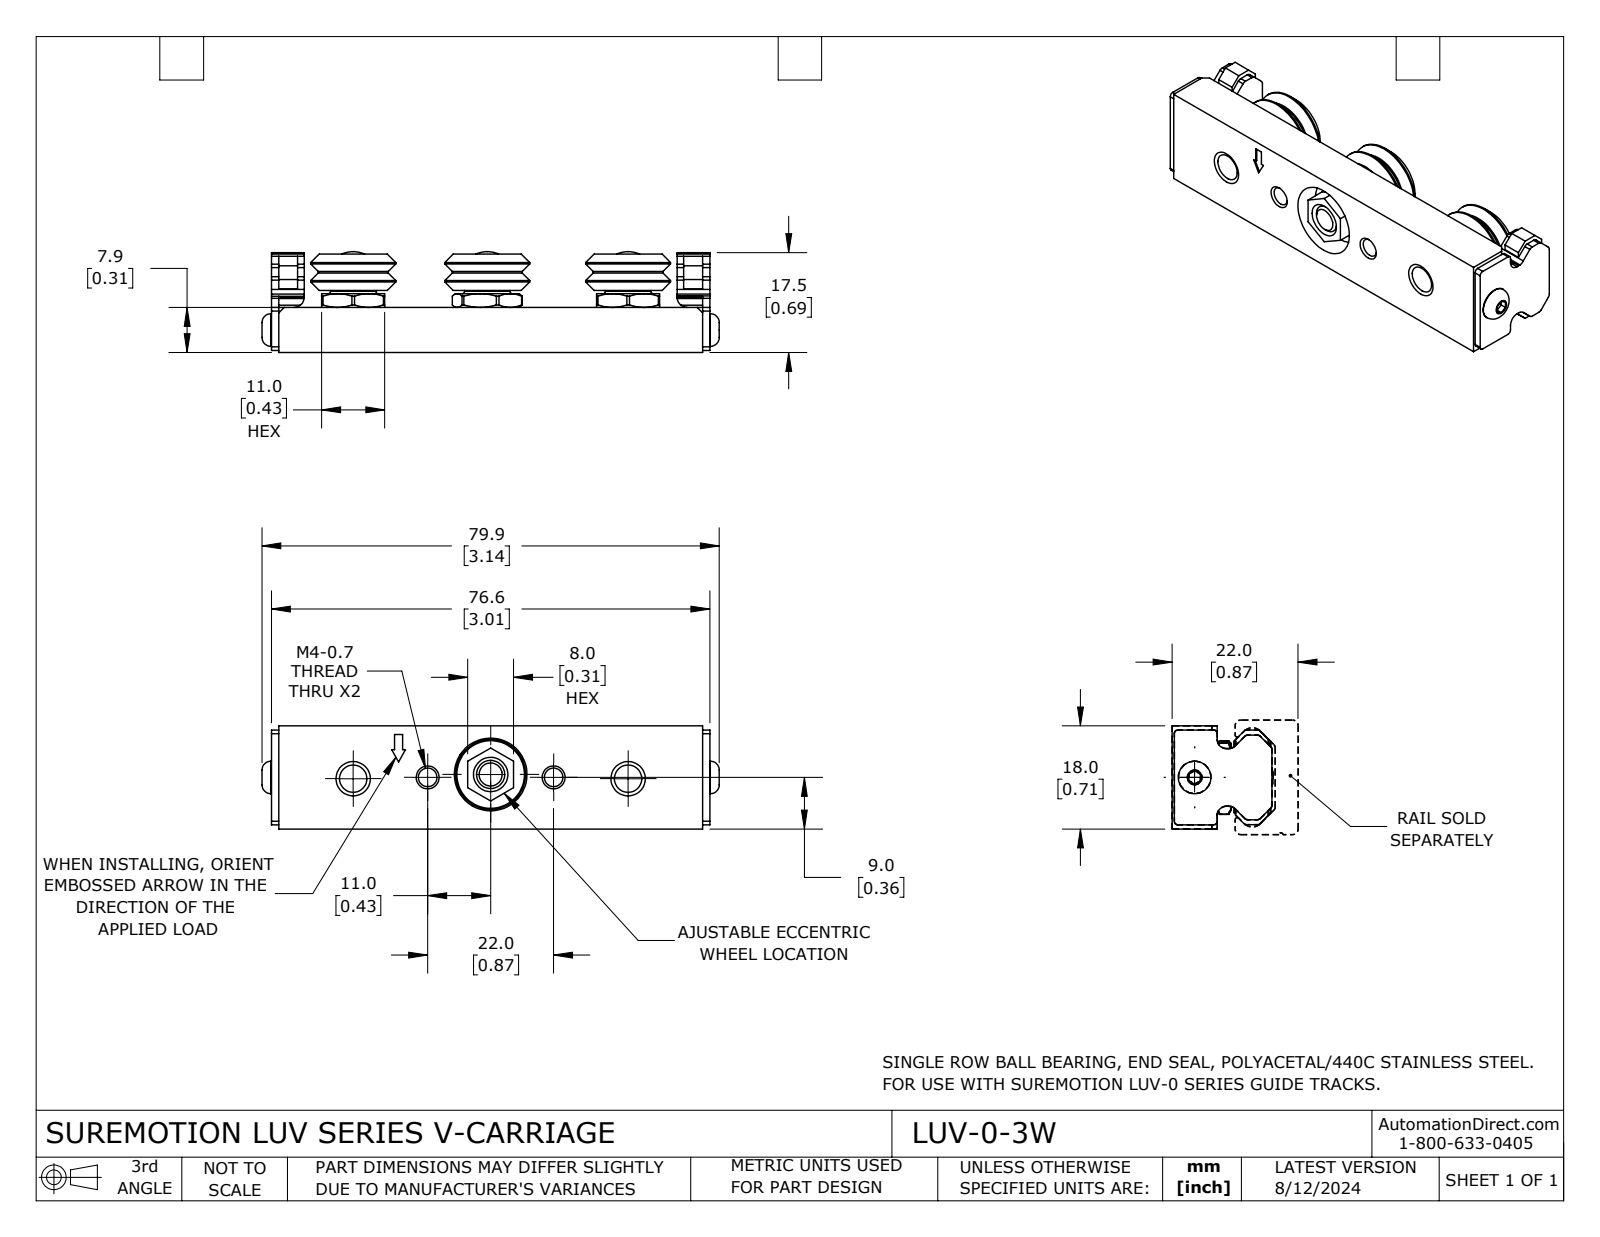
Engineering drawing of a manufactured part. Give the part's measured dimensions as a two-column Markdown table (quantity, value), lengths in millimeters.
| quantity | value |
| --- | --- |
| part name | LUV-0-3W |
| STEP written by | SolidWorks 2023 (CONFIG_CONTROL_DESIGN) |
| units | millimeters |
| bodies | 7 solids, 666 faces (217 planar, 204 cylindrical, 245 other) |
| overall size | 79.86 × 18.01 × 17.63 |
| volume | 15 269 mm³ |
| surface area | 10 324 mm² |
| round holes (diameter × count) | 4 × 3, 9.18 × 3, 9.44 × 3, 3.24 × 2, 4.92 × 2, 2.46 × 1, 4.92 × 1, 5.63 × 1, 12.7 × 1 |
| round bosses / shafts (diameter × count) | 14.83 × 3, 7.92 × 3, 6.22 × 3, 3.99 × 3, 6.48 × 2, 6 × 2, 4.5 × 2, 11.81 × 1 |
| partial cylindrical surfaces (radius × count) | 0.38 × 12, 0.84 × 6, 0.64 × 4, 1.6 × 4, 6.22 × 3, 1.78 × 2 |
| main face-to-face distances | 7.87, 18, 1.27, 75.29, 6.35, 74.02, 76.56, 5.72, 70.84, 4.45 |
| hole center spacings | 11.01, 13, 24.01, 35, 0.61, 10.42, 11.6, 22 |
